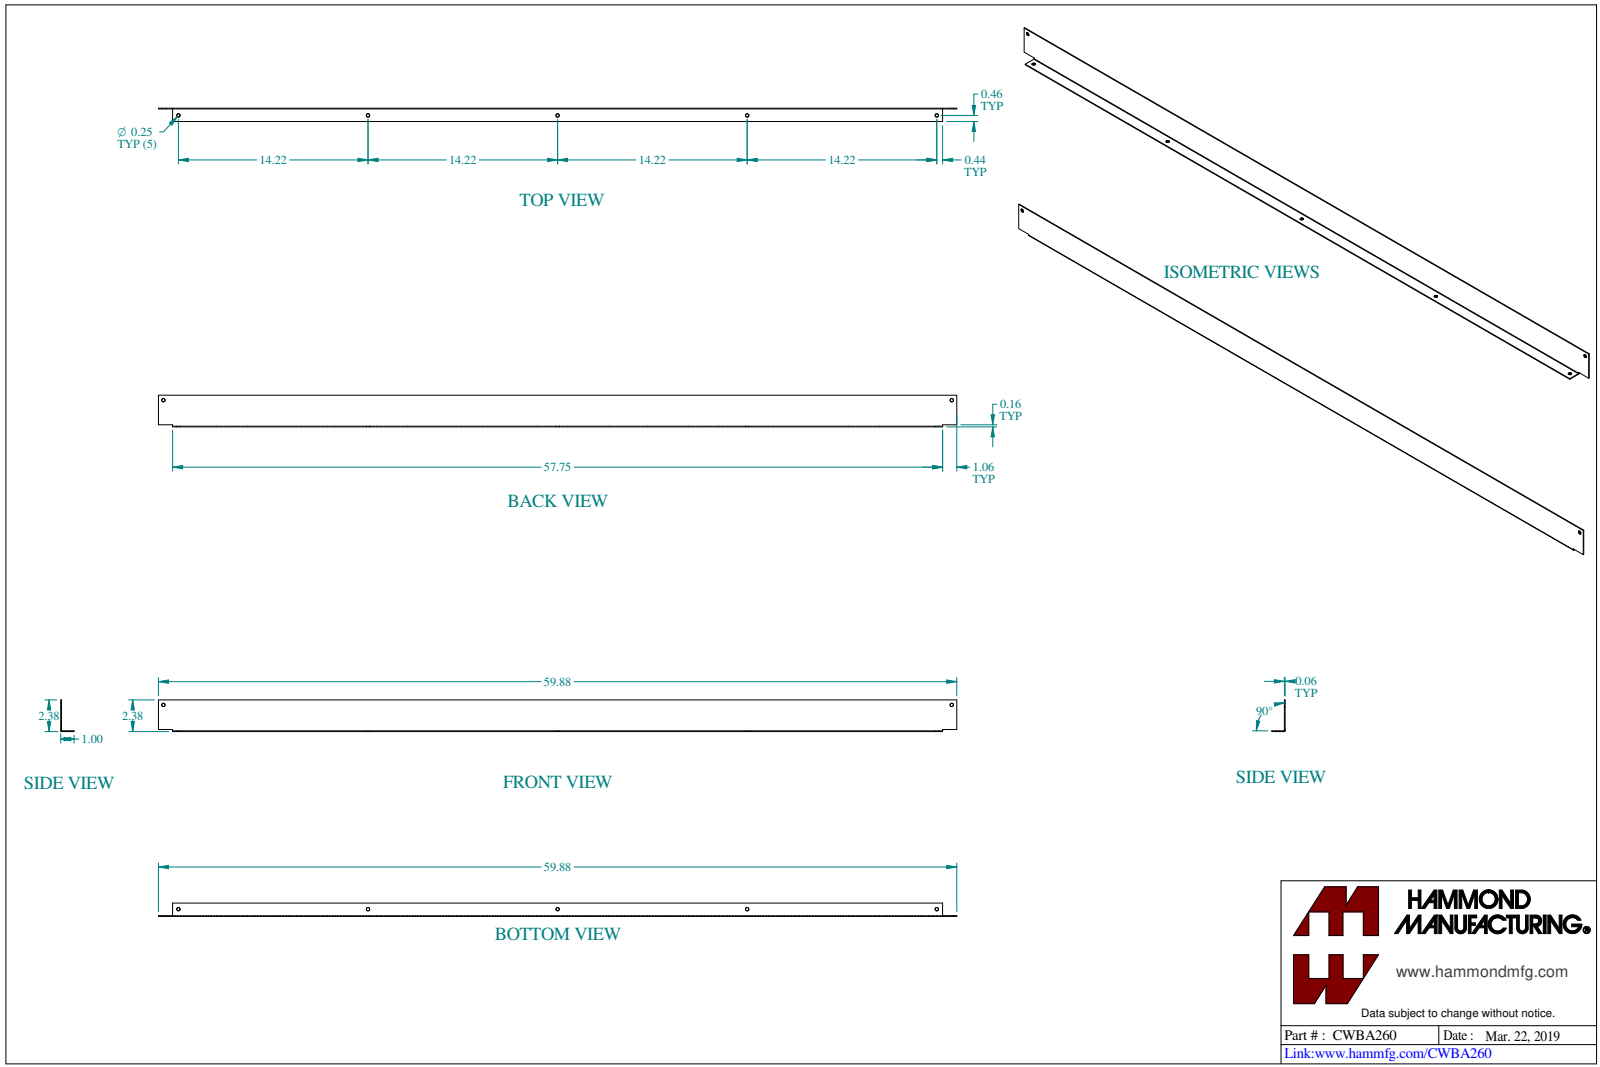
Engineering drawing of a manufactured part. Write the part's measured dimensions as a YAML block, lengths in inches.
part_name: "CWBA260"
step_written_by: "SolidWorks 2023 (CONFIG_CONTROL_DESIGN)"
units: inches
bodies: {solids: 3, faces: 63, planar: 35, cylindrical: 22, other: 6}
overall_size: [59.875, 2.818, 1]
volume: 11.12
surface_area: 397.7
round_holes:
  - {diameter: 0.25, count: 7}
  - {diameter: 0.156, count: 1}
round_bosses_or_shafts:
  - {diameter: 0.367, count: 1}
  - {diameter: 0.19, count: 1}
partial_cylinders:
  - {radius: 0.029, count: 1}
  - {radius: 0.086, count: 1}
face_to_face_distances: [0.057, 2.375, 2.318, 1, 0.943, 59.875, 1.063, 58.812, 0.156, 0.099]
hole_center_spacings: [14.219, 14.219, 28.437, 42.656, 28.438, 56.875, 59.125]
